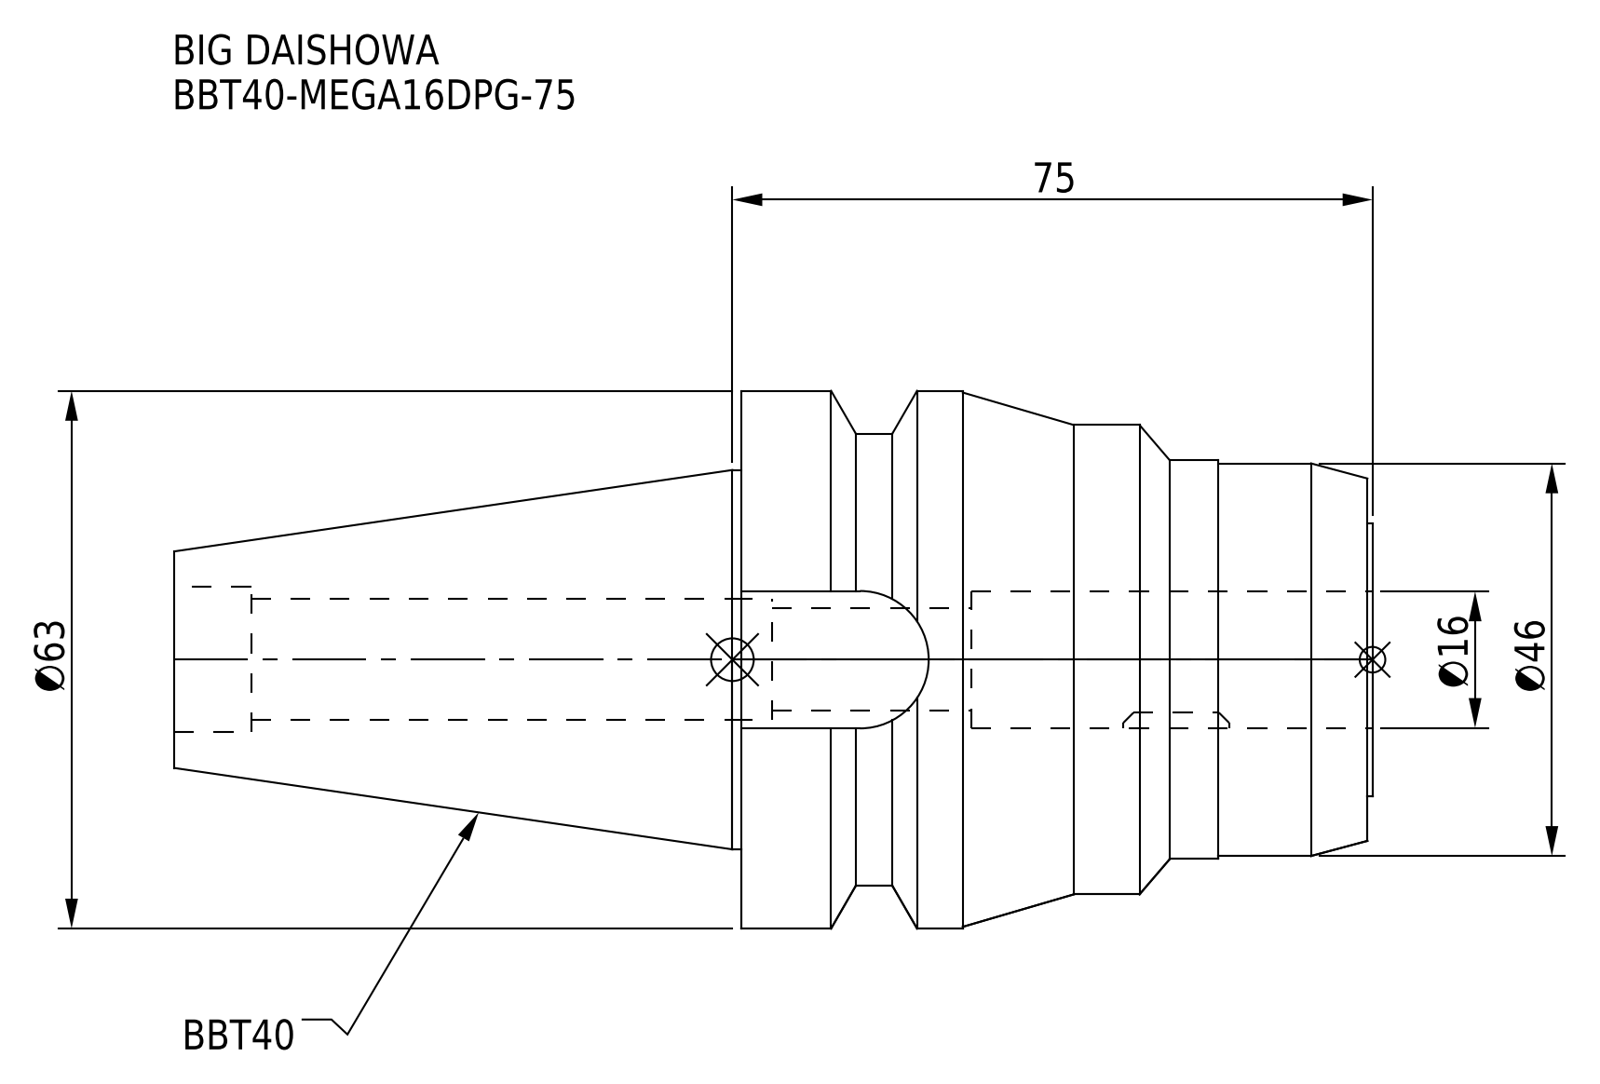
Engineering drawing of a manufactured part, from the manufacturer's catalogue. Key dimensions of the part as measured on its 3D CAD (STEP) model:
Part name (STEP PRODUCT): BBT40-MEGA16DPG-75
STEP written by: CREO PARAMETRIC BY PTC INC, 2016380 (AUTOMOTIVE_DESIGN)
Units: millimetres
Bodies: 1 solid, 55 faces (15 planar, 28 cylindrical, 12 other)
Overall size (bounding box): 140.4 × 63 × 63
Volume: 211 070 mm³ · Surface area: 31 540 mm²
Round holes (diameter × count): ⌀12 ×1, ⌀14.2 ×1, ⌀16 ×1, ⌀17 ×1
Round bosses / shafts (diameter × count): ⌀63 ×1, ⌀55 ×1, ⌀53 ×1, ⌀46.7 ×1, ⌀46 ×1, ⌀44.45 ×1, ⌀31.9 ×1
Partial cylindrical surfaces — rounded edges, fillets, slot ends (radius × count): R8.05 ×1
Main face-to-face distances: 73.4, 0.6, 74, 45, 140.4, 139.8, 66.4, 16.1, 47, 46.4
